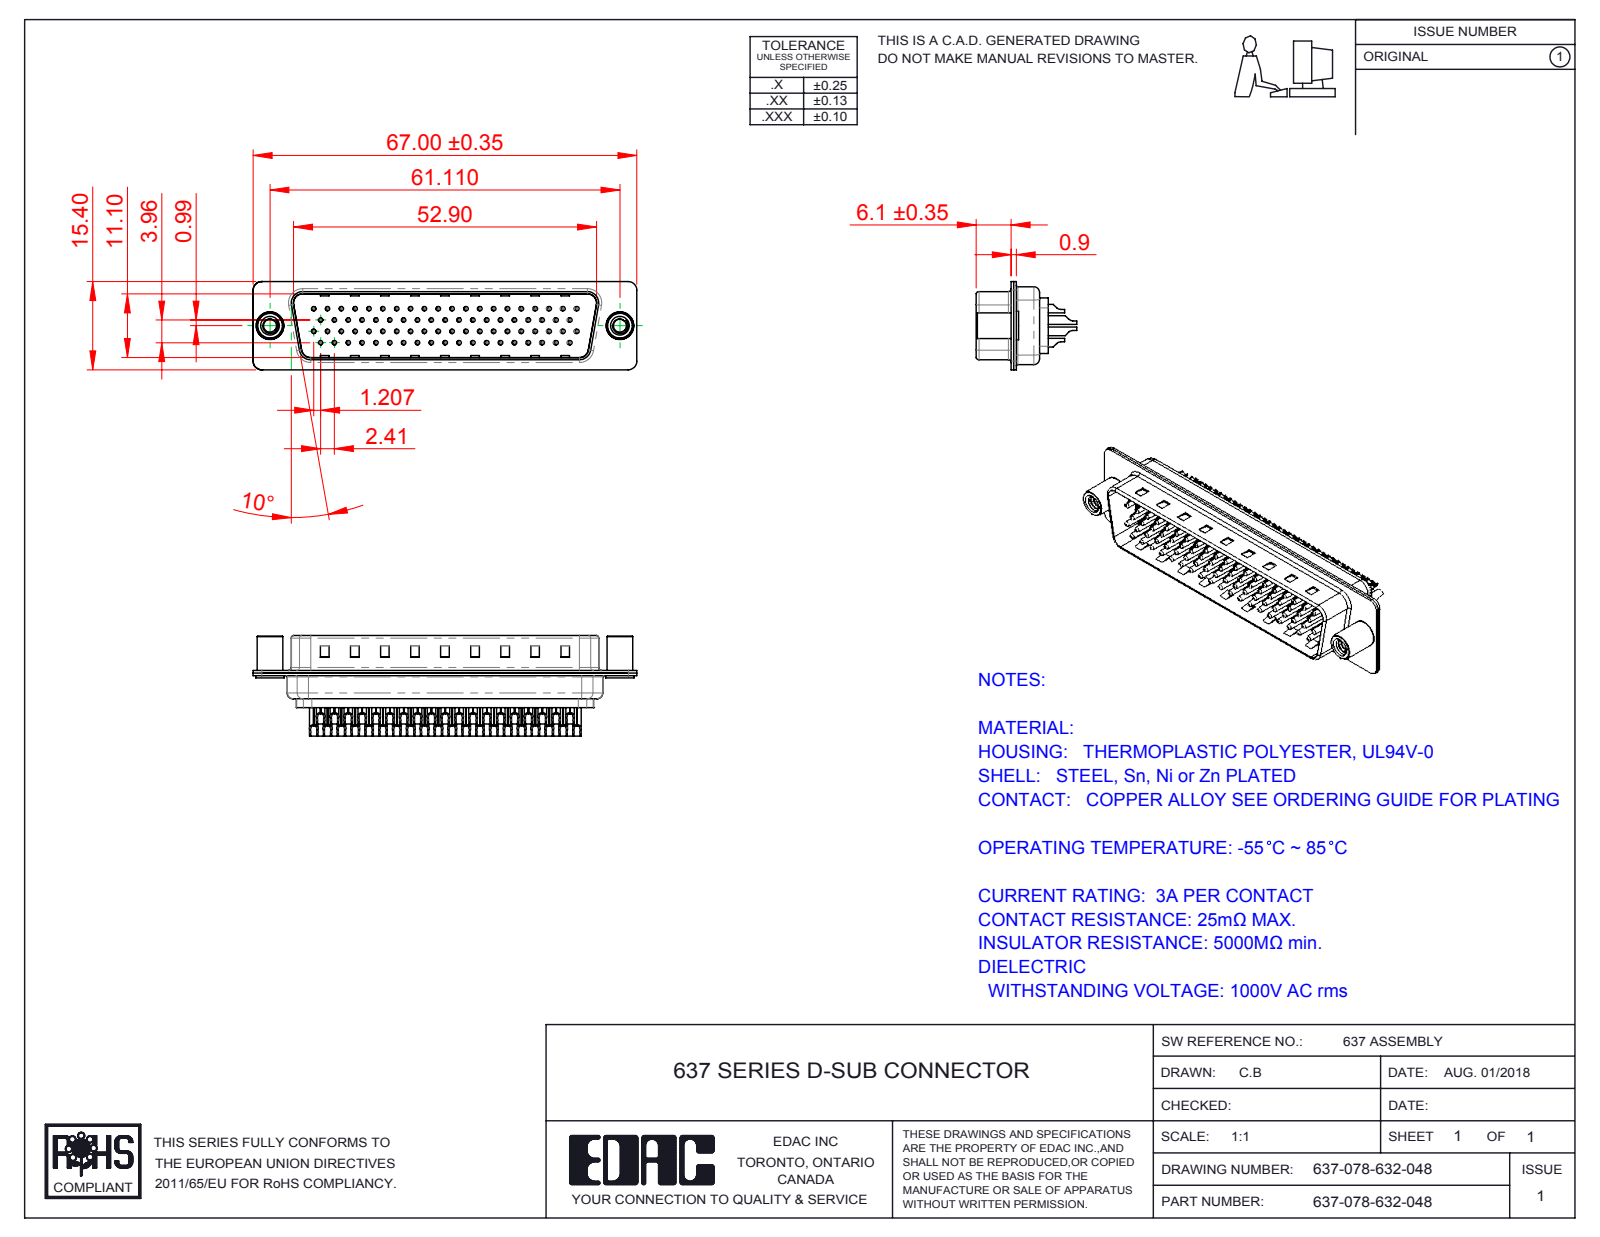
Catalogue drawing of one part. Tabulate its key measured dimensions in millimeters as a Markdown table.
| quantity | value |
| --- | --- |
| part name | 637 Contact Row 3_32; 637 Contact Row 2_32(78); 637-078-632-048; 637 Shell Front_78 Contacts (+5 more) |
| STEP written by | SolidWorks 2016 (CONFIG_CONTROL_DESIGN) |
| units | millimeters |
| bodies | 83 solids, 5438 faces (1297 planar, 2431 cylindrical, 1710 other) |
| overall size | 67 × 17.55 × 15.4 |
| volume | 4 497 mm³ |
| surface area | 16 973 mm² |
| round holes (diameter × count) | 1.6 × 150, 0.35 × 78, 1.1 × 78, 0.75 × 72, 2 × 72, 4 × 3, 2.26 × 2, 4.8 × 2 |
| round bosses / shafts (diameter × count) | 2 × 78, 1.5 × 78, 0.75 × 78, 5 × 2, 4.9 × 2, 4.5 × 2, 4.8 × 1 |
| partial cylindrical surfaces (radius × count) | 1.5 × 16, 2 × 12, 0.5 × 8, 1 × 8, 0.25 × 4, 0.55 × 4, 0.7 × 4, 0.95 × 4 |
| main face-to-face distances | 0.45, 0.4, 1.5, 1.95, 11.9, 11.5, 0.7, 11.1, 0.9, 0.8 |
| hole center spacings | 2.41, 7.24, 6.06, 9.65, 6.96, 8.46, 14.54, 16.89 |
